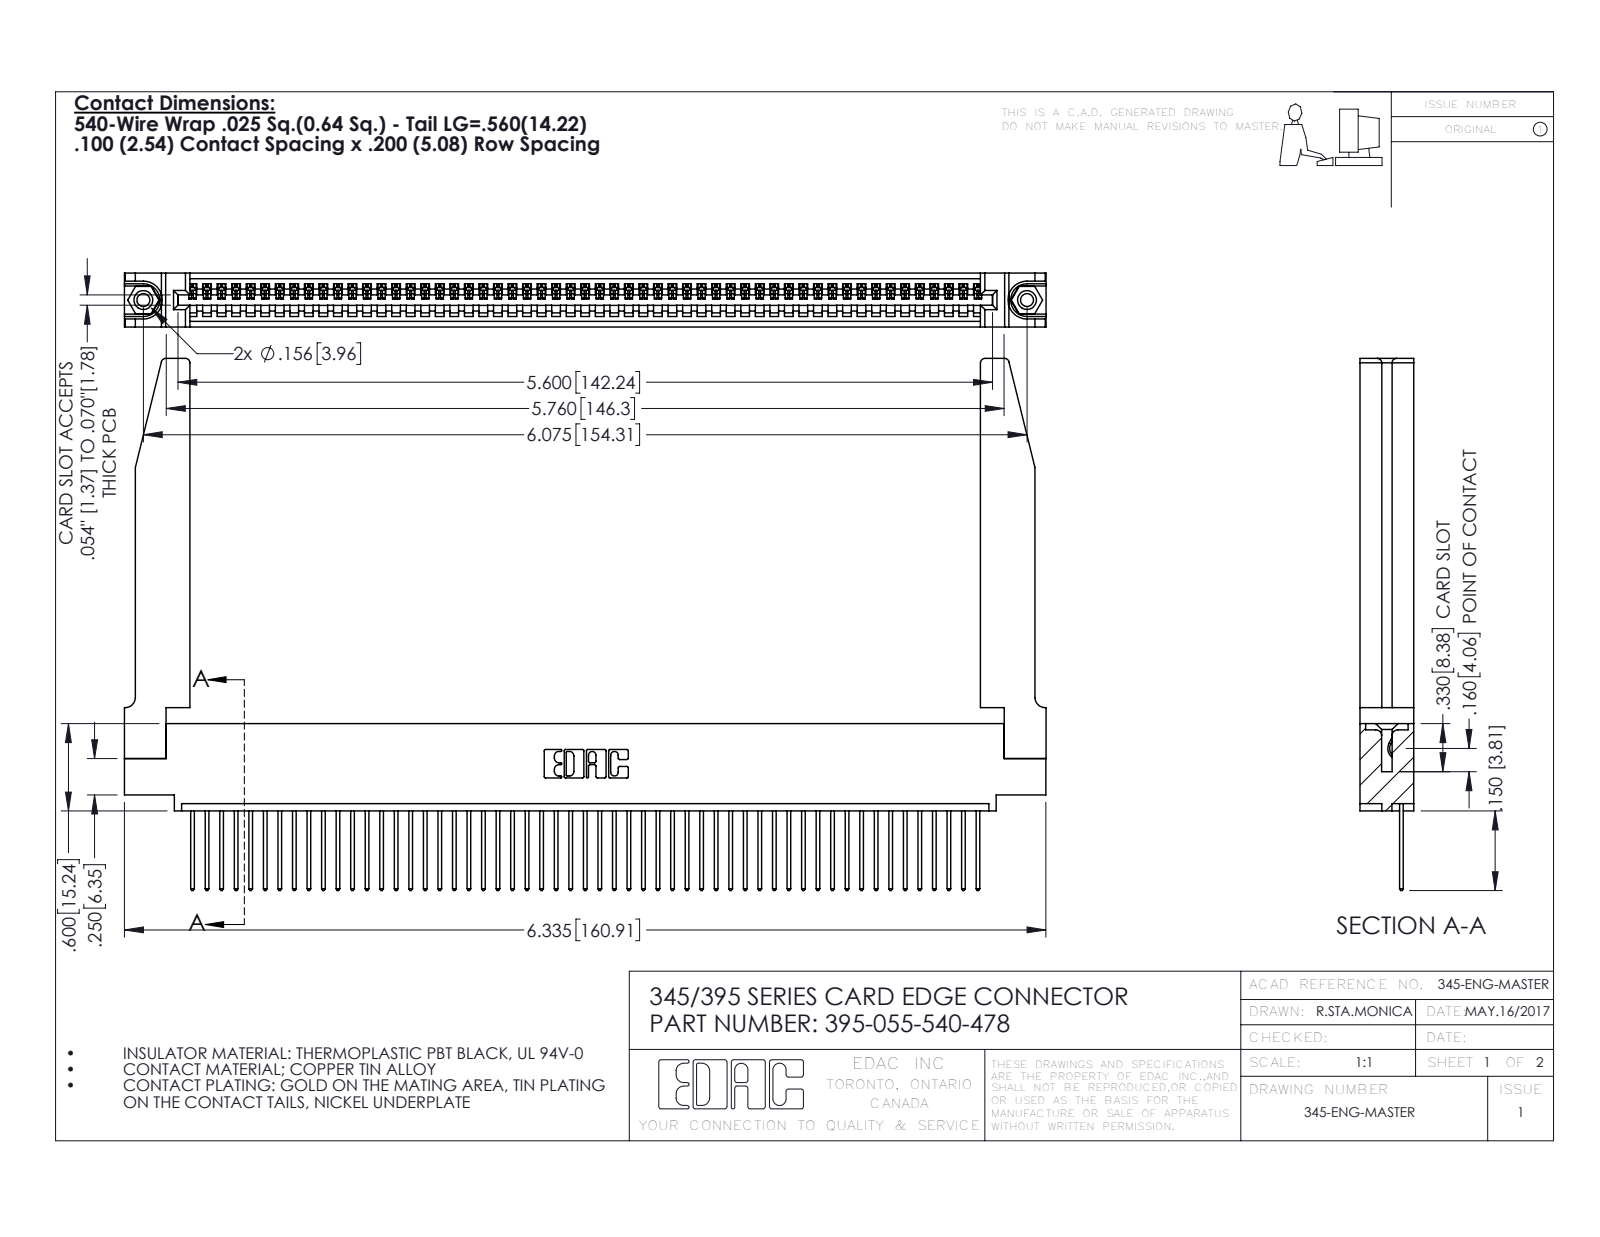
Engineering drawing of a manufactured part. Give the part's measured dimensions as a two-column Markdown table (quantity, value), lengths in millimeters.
| quantity | value |
| --- | --- |
| part name | 395-055-540-478; 345 Part_0.110 Offset - 0.156 Dia-TH; 345-220-078_345-220-078; 345-250-001_345-250-001-102 (+1 more) |
| STEP written by | SolidWorks 2016 (CONFIG_CONTROL_DESIGN) |
| units | millimeters |
| bodies | 60 solids, 3554 faces (2426 planar, 1076 cylindrical, 52 other) |
| overall size | 160.9 × 92.9 × 9.4 |
| volume | 23 170 mm³ |
| surface area | 28 100 mm² |
| round holes (diameter × count) | 2.3 × 2, 3.2 × 2, 4 × 2, 1.6 × 1 |
| round bosses / shafts (diameter × count) | 3.9 × 2 |
| partial cylindrical surfaces (radius × count) | 0.2 × 110, 0.3 × 110, 0.3 × 22, 0.8 × 8, 0.2 × 6, 0.8 × 6, 0.7 × 3, 0.8 × 2 |
| main face-to-face distances | 1.8, 9.4, 7.6, 2.5, 6.9, 0.6, 5.1, 5.7, 3.8, 3.8 |
| hole center spacings | 6.9, 148.3, 154.3 |
